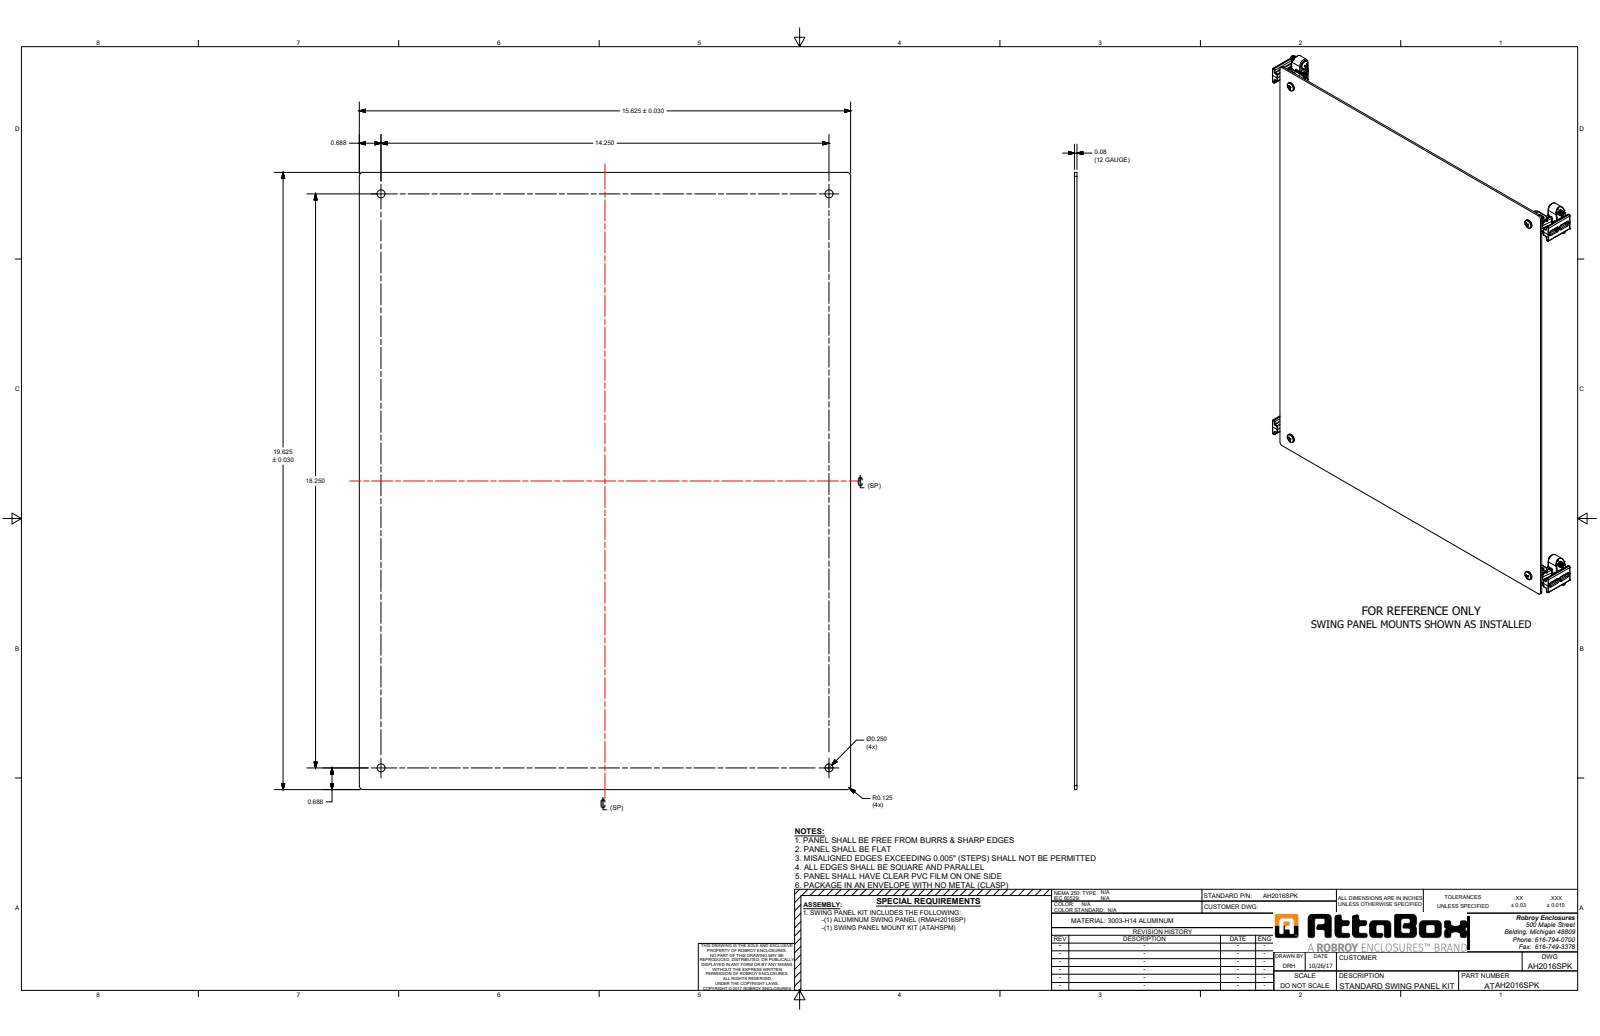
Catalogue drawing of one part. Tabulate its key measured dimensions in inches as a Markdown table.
| quantity | value |
| --- | --- |
| part name | AH2016SPK |
| STEP written by | SolidWorks 2019 (AUTOMOTIVE_DESIGN) |
| units | inches |
| bodies | 33 solids, 2010 faces (518 planar, 736 cylindrical, 756 other) |
| overall size | 19.625 × 16.559 × 1.448 |
| volume | 27.6 in³ |
| surface area | 676.2 in² |
| round holes (diameter × count) | 0.156 × 8, 0.25 × 8 |
| round bosses / shafts (diameter × count) | 0.373 × 8, 0.262 × 8, 0.19 × 8 |
| partial cylindrical surfaces (radius × count) | 0.035 × 248, 0.02 × 124, 0.065 × 52, 0.015 × 30, 0.045 × 16, 0.05 × 16, 0.025 × 14, 0.9 × 8 |
| main face-to-face distances | 0.08, 0.31, 18.25, 15.625, 0.5, 19.625, 0.51, 0.59, 16.559, 0.3 |
| hole center spacings | 18.25, 0.875, 14.25, 23.154, 17.375, 19.125 |
